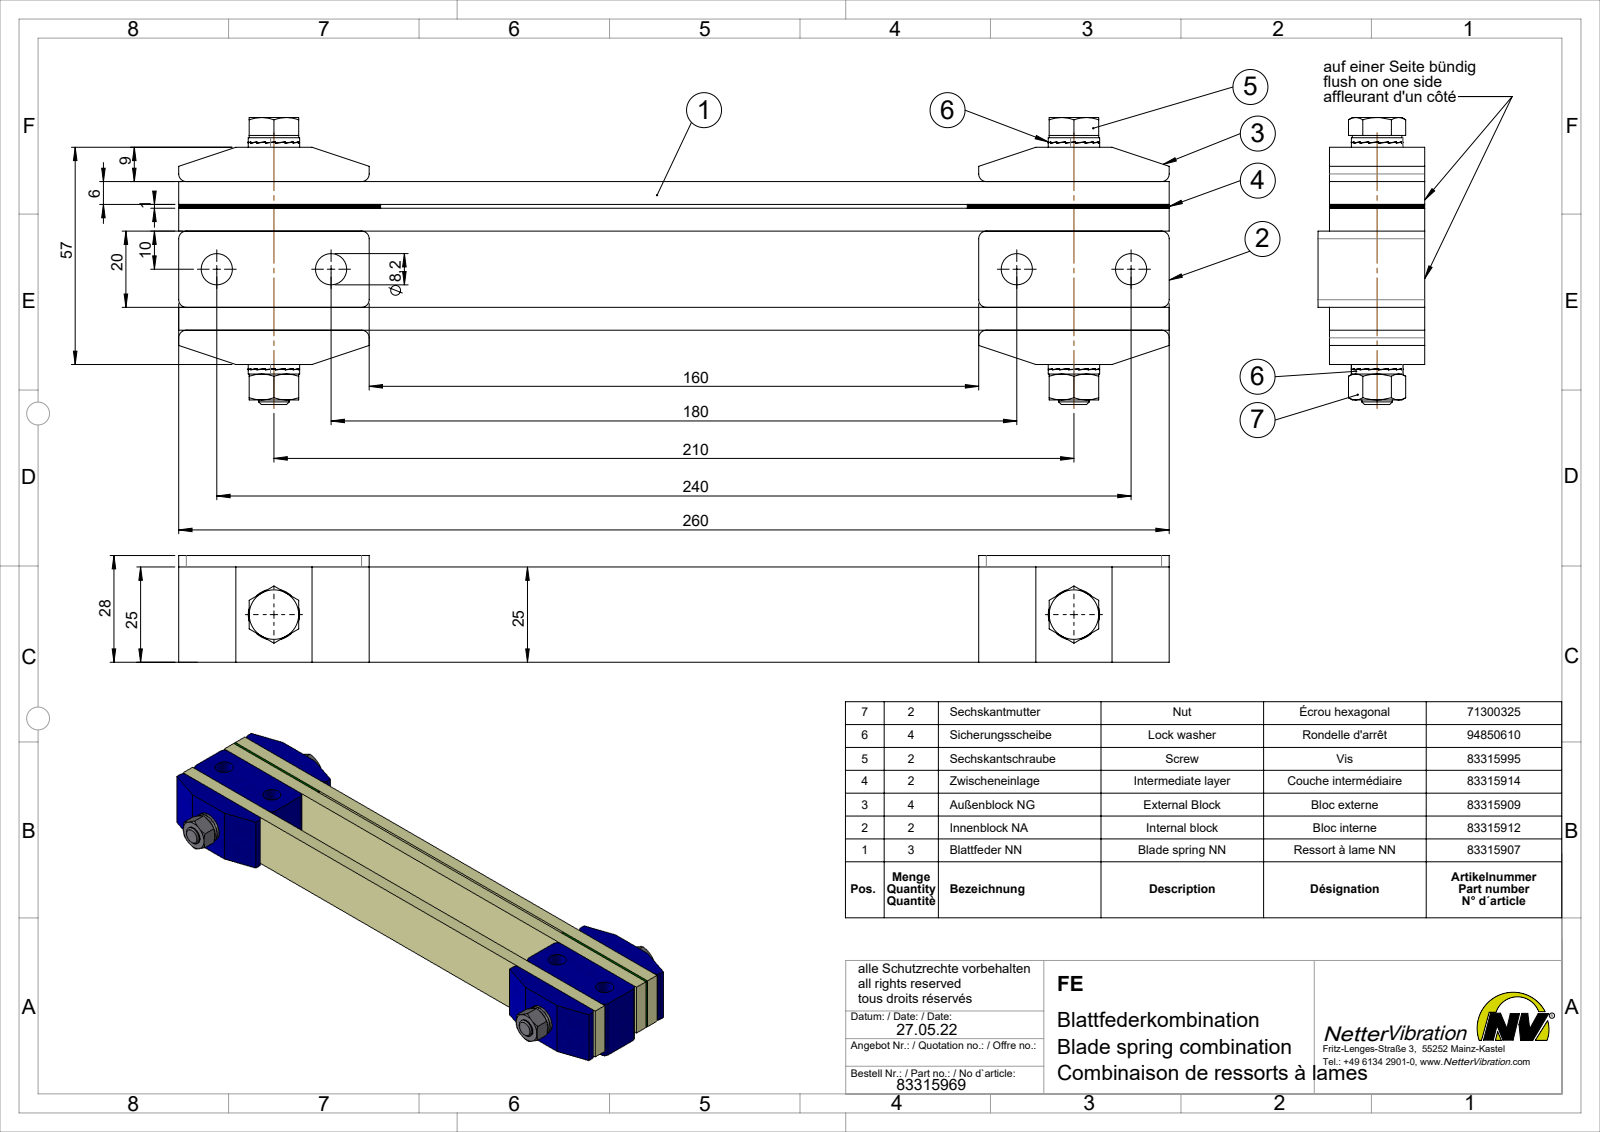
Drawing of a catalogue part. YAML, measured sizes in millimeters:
part_name: "Blattfederkombination FE # 83315969"
step_written_by: "SolidWorks 2015 (AUTOMOTIVE_DESIGN)"
units: millimeters
bodies: {solids: 19, faces: 720, planar: 576, cylindrical: 92, other: 52}
overall_size: [260, 75.3, 28]
volume: 211573
surface_area: 91558
round_holes:
  - {diameter: 8.2, count: 6}
  - {diameter: 6.8, count: 2}
  - {diameter: 8, count: 2}
  - {diameter: 8.5, count: 2}
  - {diameter: 8.7, count: 2}
round_bosses_or_shafts:
  - {diameter: 13.5, count: 2}
  - {diameter: 13, count: 2}
partial_cylinders:
  - {radius: 2, count: 16}
face_to_face_distances: [6, 7, 26, 33, 13, 1, 27, 20, 39, 32]
hole_center_spacings: [210, 30, 180, 240]
